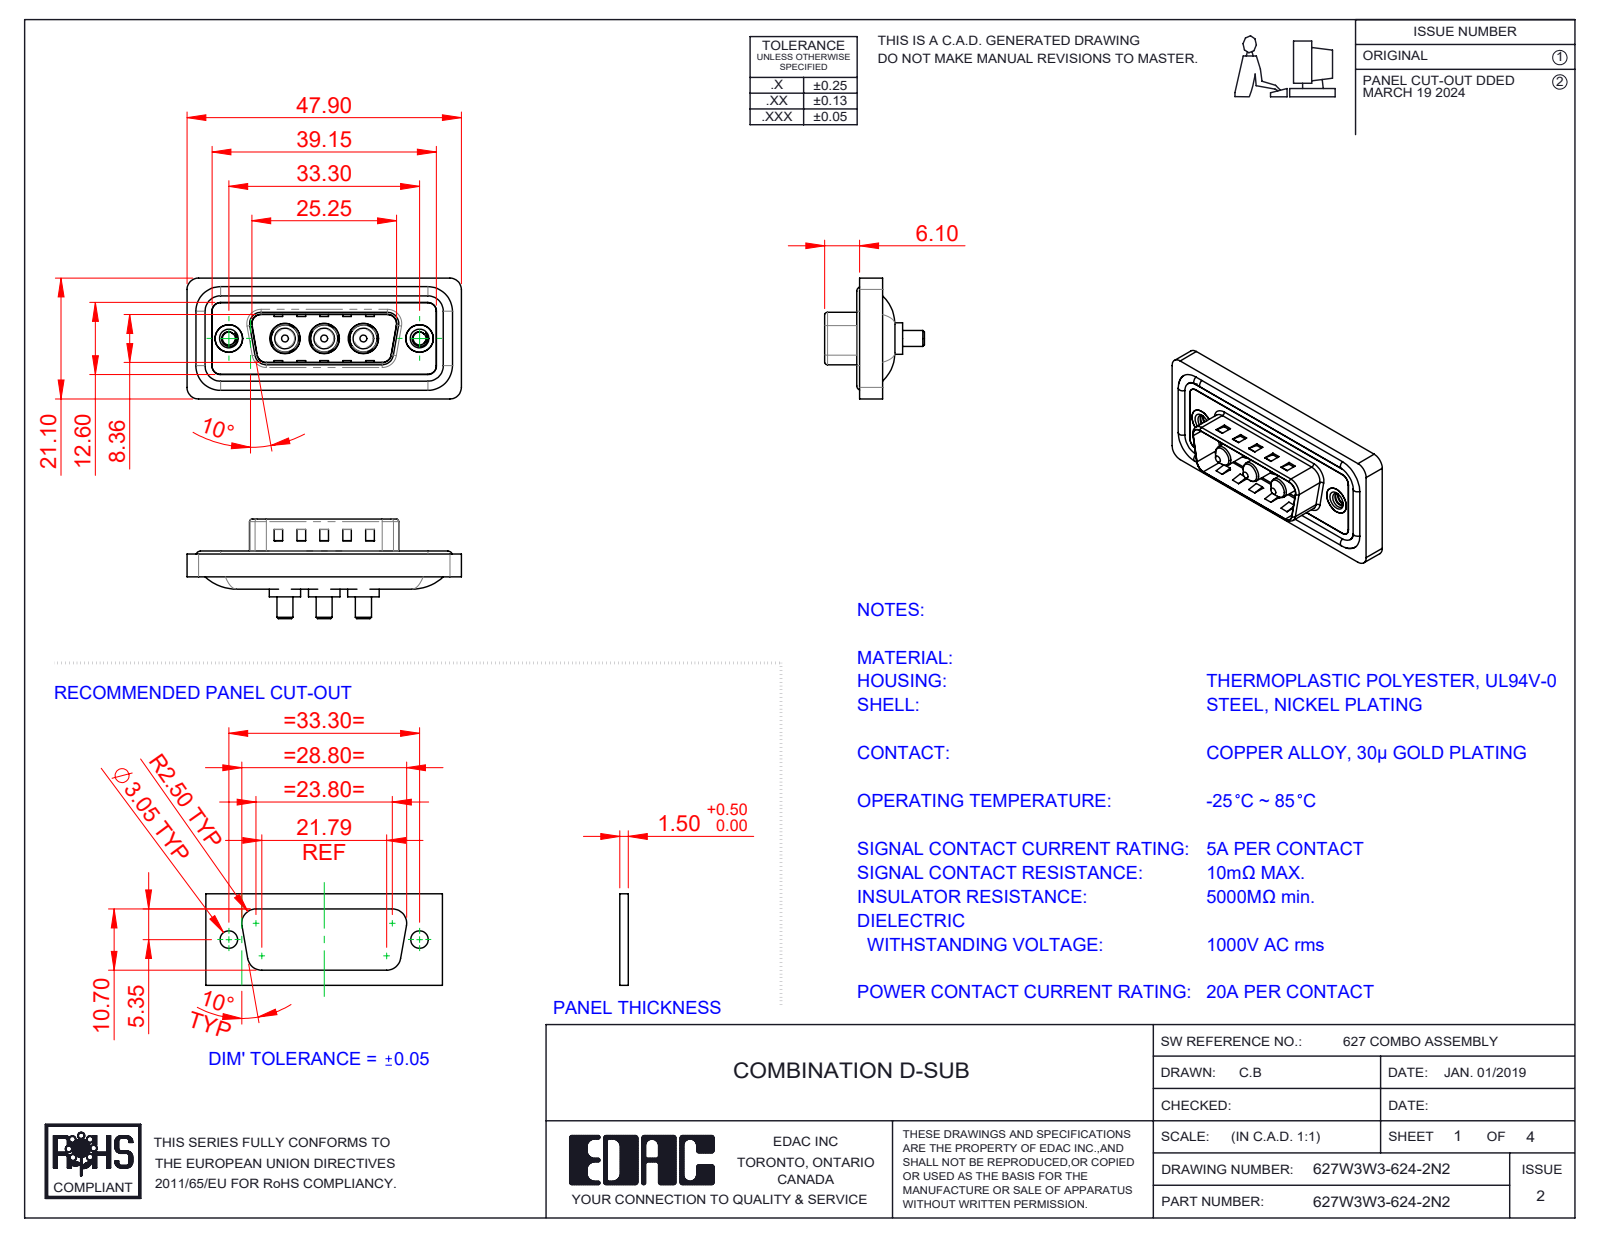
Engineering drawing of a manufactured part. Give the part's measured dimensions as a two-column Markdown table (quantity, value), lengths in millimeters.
| quantity | value |
| --- | --- |
| part name | 627Combo Waterproof Housing_15 Contacts; 627Combo Shell Rear_15 Contacts; Power Pin_20A S; 627W3W3-624-2N2 (+3 more) |
| STEP written by | SolidWorks 2023 (CONFIG_CONTROL_DESIGN) |
| units | millimeters |
| bodies | 13 solids, 564 faces (207 planar, 241 cylindrical, 116 other) |
| overall size | 47.9 × 21.1 × 17.4 |
| volume | 5 586 mm³ |
| surface area | 8 753 mm² |
| round holes (diameter × count) | 4.85 × 3, 5.3 × 3, 2.26 × 2, 4 × 2, 4.8 × 2, 5 × 2 |
| round bosses / shafts (diameter × count) | 1.6 × 4, 5.5 × 3, 5.2 × 3, 4.75 × 3, 3.75 × 3, 3.6 × 3, 2.8 × 3, 4.9 × 2 |
| partial cylindrical surfaces (radius × count) | 1.5 × 26, 2 × 20, 0.5 × 8, 1.6 × 8, 0.25 × 4, 0.6 × 4, 0.65 × 4, 0.9 × 4 |
| main face-to-face distances | 0.4, 1.1, 1.5, 0.5, 1.6, 3.1, 2.9, 4, 0.82, 9.58 |
| hole center spacings | 6.85, 9.8, 16.65, 23.5, 13.7, 33.3 |
